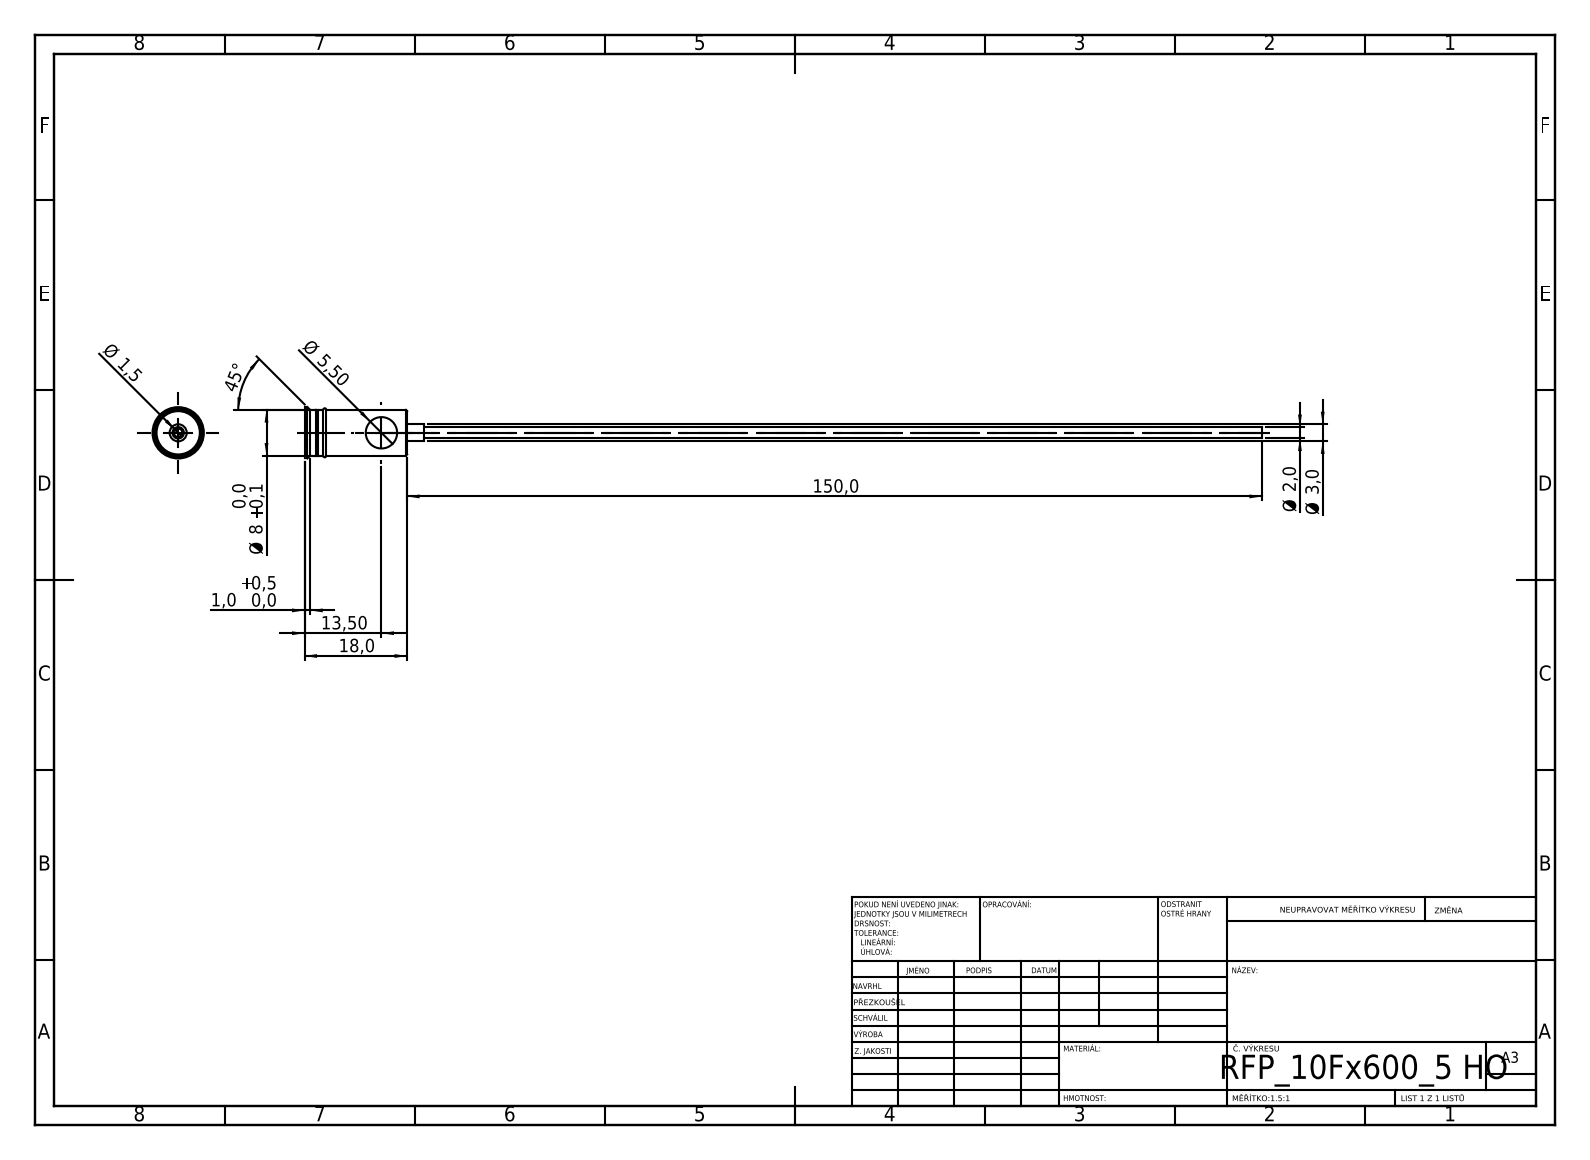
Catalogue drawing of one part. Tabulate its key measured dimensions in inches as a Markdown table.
| quantity | value |
| --- | --- |
| STEP written by | SolidWorks 2019 (CONFIG_CONTROL_DESIGN) |
| units | inches |
| bodies | 1 solid, 44 faces (20 planar, 16 cylindrical, 8 other) |
| overall size | 6.614 × 0.354 × 0.354 |
| volume | 0.057 in³ |
| surface area | 3.638 in² |
| round holes (diameter × count) | 0.059 × 1, 0.217 × 1 |
| round bosses / shafts (diameter × count) | 0.354 × 1, 0.315 × 1, 0.118 × 1, 0.079 × 1 |
| main face-to-face distances | 0.709, 0.134, 0.63, 0.079, 0.618, 0.091, 0.118, 0.736, 0.748, 0.827 |
